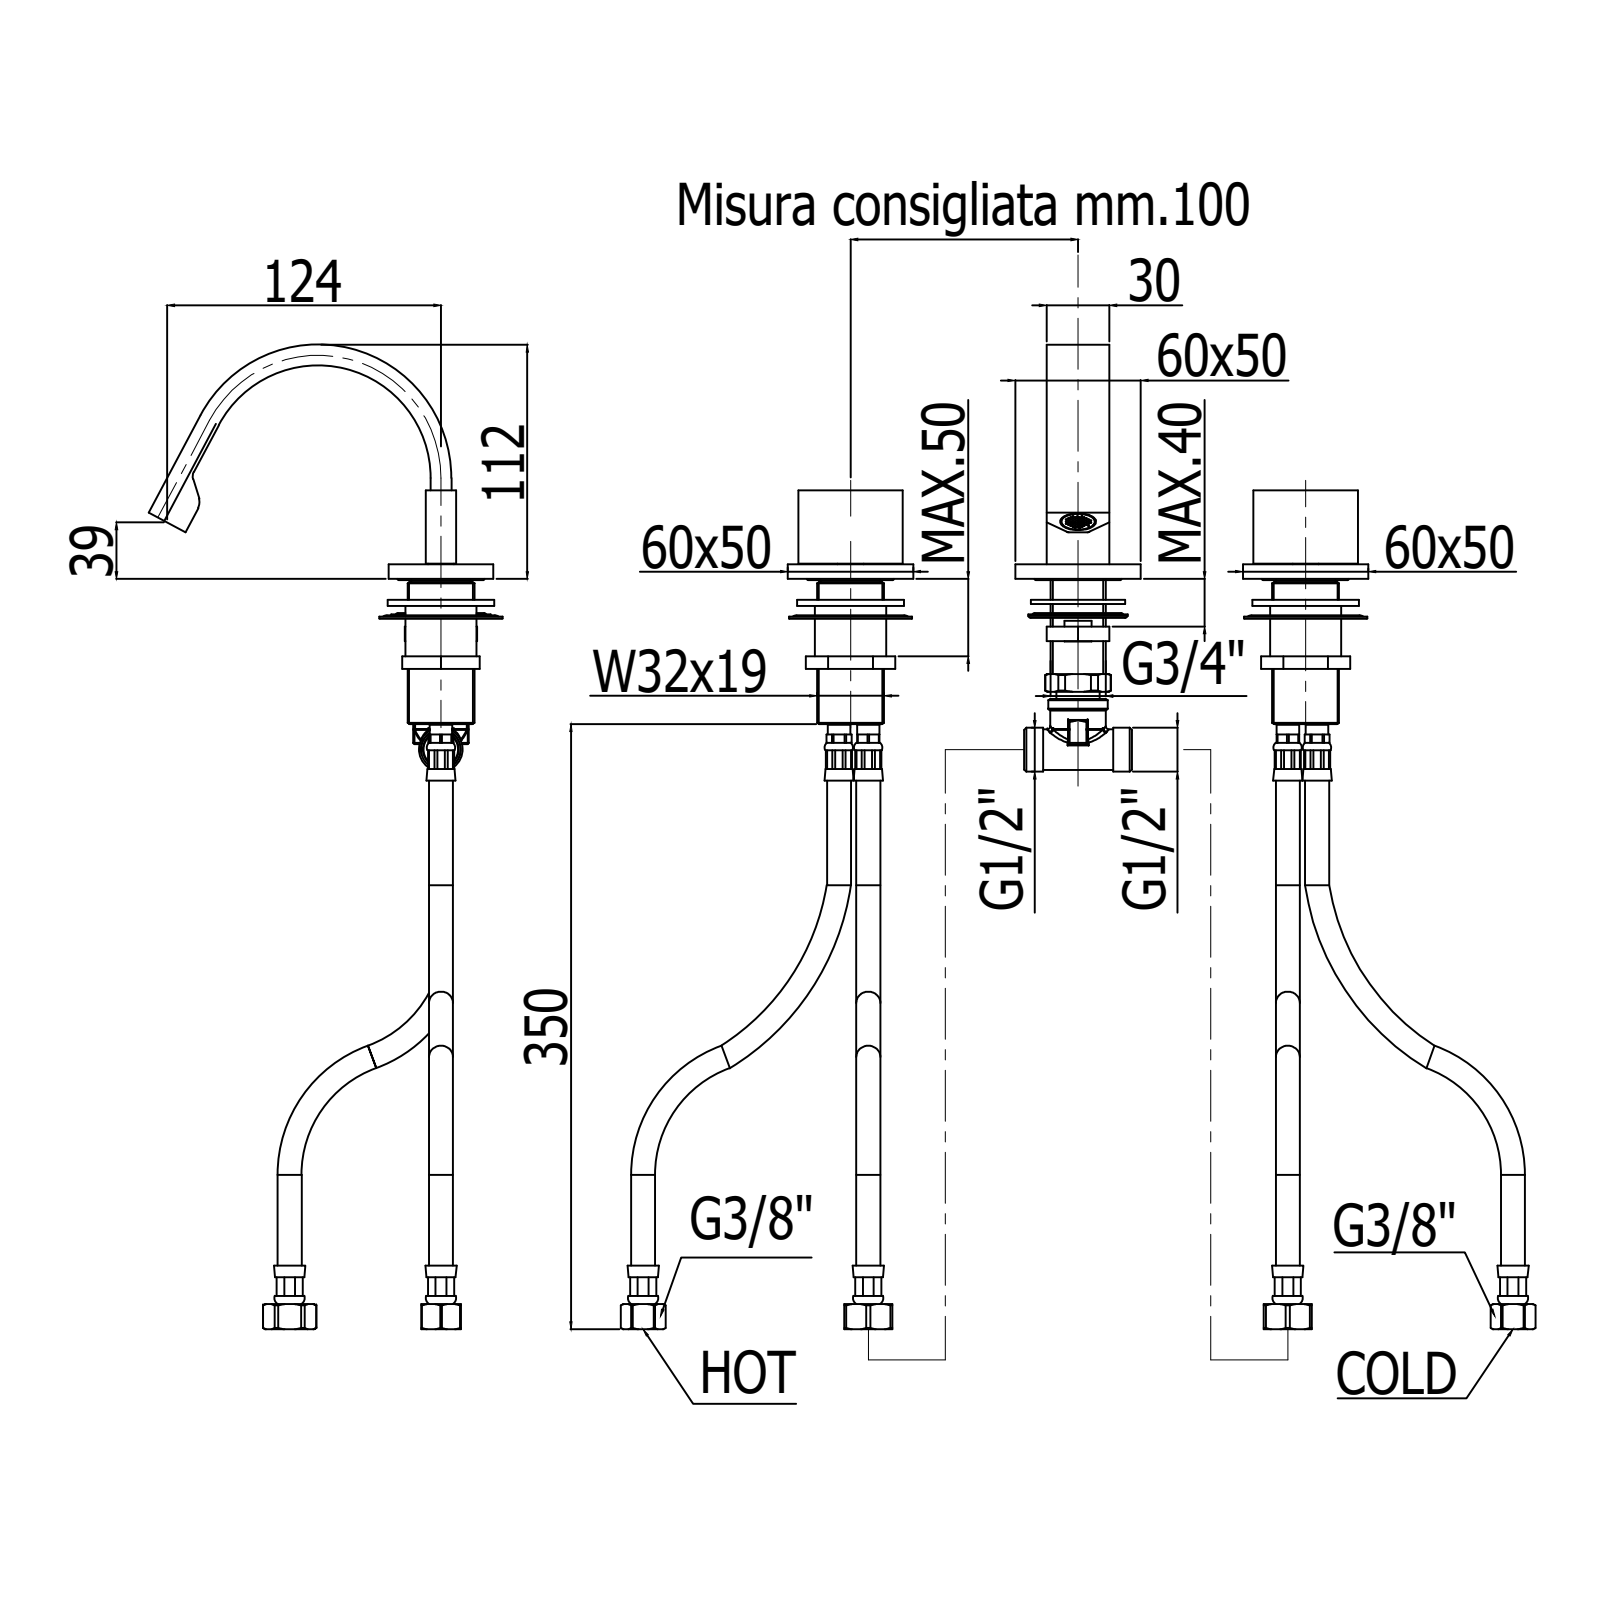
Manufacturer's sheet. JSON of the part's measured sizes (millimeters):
{"part_name": "LEP119CR", "step_written_by": "CREO PARAMETRIC BY PTC INC, 2020044 (CONFIG_CONTROL_DESIGN)", "units": "millimeters", "bodies": {"solids": 8, "faces": 2824, "planar": 2101, "cylindrical": 466, "other": 257}, "overall_size": [360, 157.83, 112], "volume_mm3": 140568, "surface_area_mm2": 78269, "round_holes": [[4.2, 4], [3.5, 3], [42, 3], [3.3, 2], [4.5, 2], [7, 2], [9, 2], [9.6, 2], [10, 2], [12.5, 2], [24.5, 2], [4.9, 1]], "round_bosses_or_shafts": [[38.5, 3], [0.9, 3], [28.5, 2], [14.2, 2], [8.9, 2], [6.8, 2], [16.4, 1], [16.38, 1]], "partial_cylinders_radius": [[0.12, 51], [0.6, 4], [3.8, 2], [9.4, 2], [1.9, 1], [7.46, 1], [52.49, 1], [53.99, 1]], "face_to_face_distances": [7, 1.5, 30, 28.5, 14.5, 8.5, 20, 2.25, 12.25, 17.75], "hole_center_spacings": [300, 10.8, 11.2, 138.8, 150, 161.2, 300.19, 22.4]}
